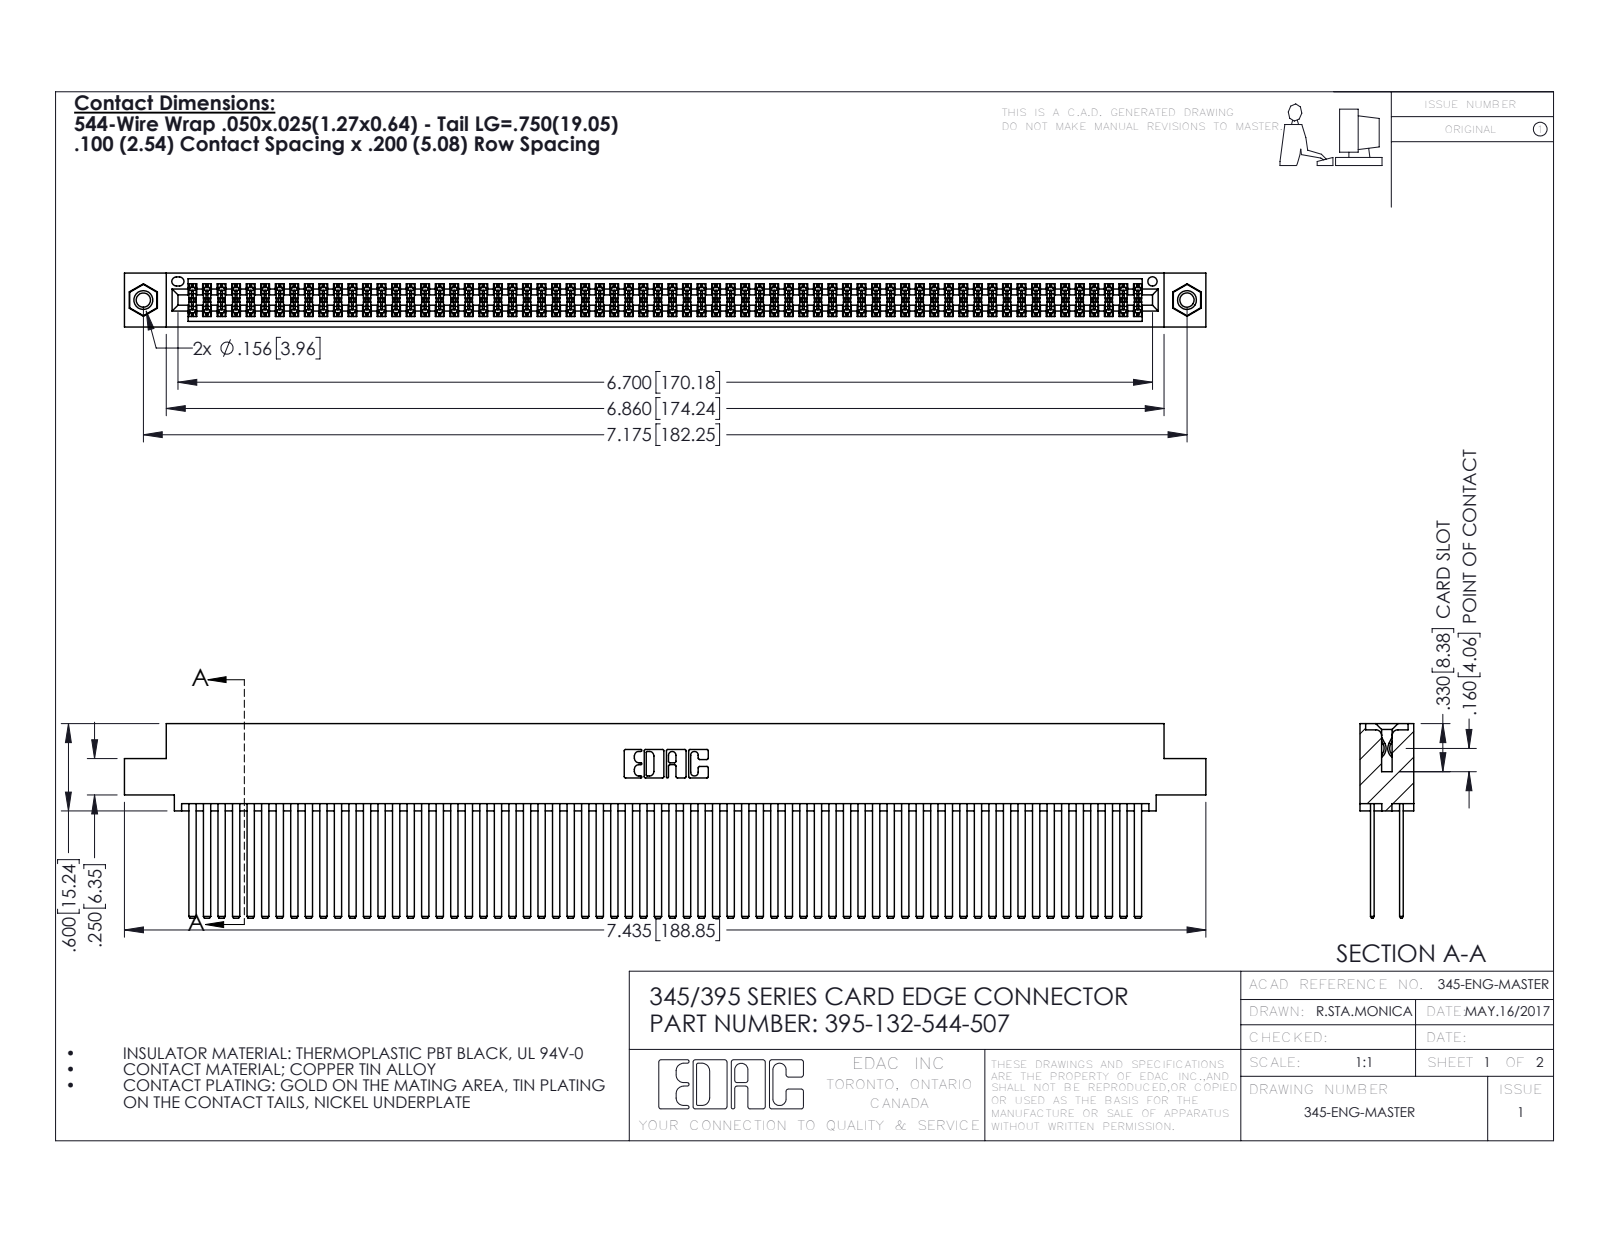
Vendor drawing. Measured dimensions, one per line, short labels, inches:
name: 395-132-544-507; 345-292-001_345-293-144; 345 Part_0.110 Offset - 0.156 Dia-TI; 345-250-001_345-250-005-103
written by: SolidWorks 2016 (CONFIG_CONTROL_DESIGN)
unit: in
bodies: 135 solids, 5998 faces (3944 planar, 2038 cylindrical, 16 other)
size: 7.435 × 1.337 × 0.37
volume: 1.241 in³; area: 55.9 in²
holes: 2× ⌀0.098, 2× ⌀0.125, 2× ⌀0.156, 1× ⌀0.064
bosses: 2× ⌀0.155
rounds: 198× R0.006, 22× R0.01, 6× R0.007, 6× R0.031, 3× R0.026, 2× R0.014, 2× R0.019, 2× R0.022
face distances: 0.2, 0.025, 0.072, 0.098, 0.272, 0.298, 0.225, 0.175, 0.37, 0.149
hole spacings: 0.27, 6.939, 7.175
